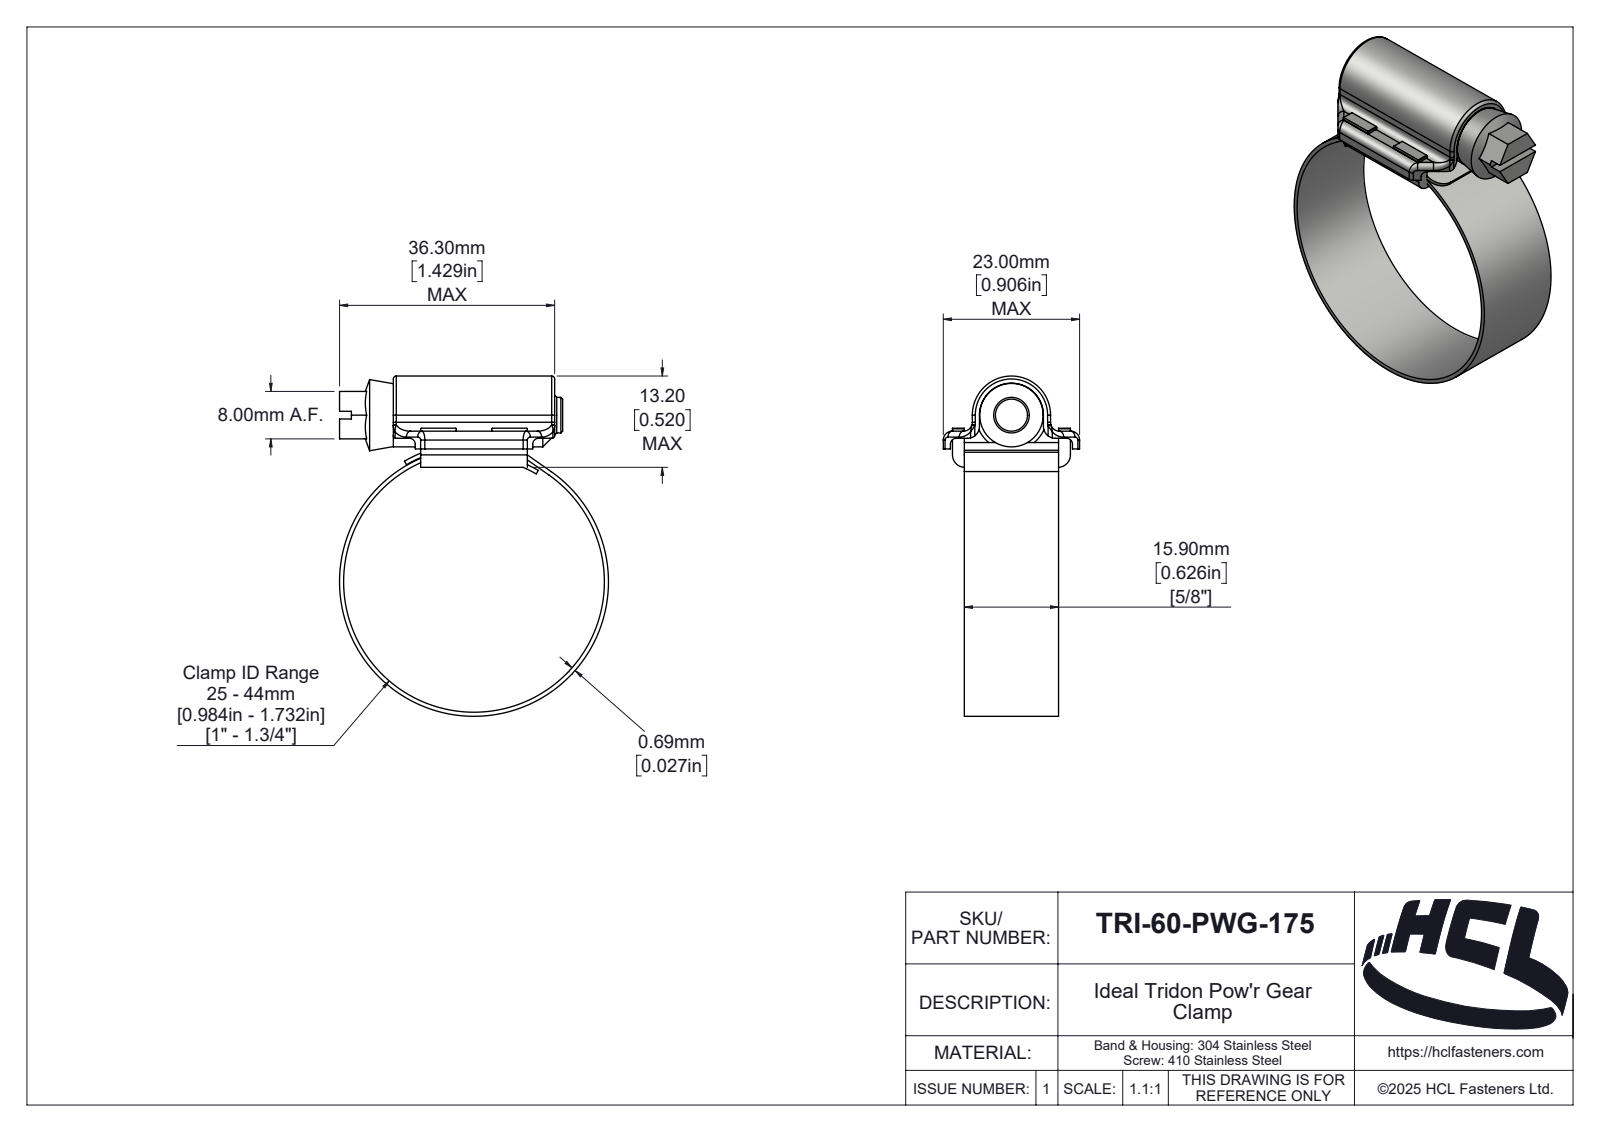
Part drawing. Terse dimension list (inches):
name: TRI-60-PWG-175
written by: SolidWorks 2025 (AUTOMOTIVE_DESIGN)
unit: in
bodies: 4 solids, 268 faces (87 planar, 102 cylindrical, 79 other)
size: 2.259 × 1.787 × 0.906
volume: 0.427 in³; area: 15.59 in²
holes: 1× ⌀1.732
bosses: 1× ⌀1.787, 1× ⌀0.421, 1× ⌀0.236
rounds: 14× R0.039, 4× R0.02, 4× R0.059, 3× R0.079, 2× R0.004, 2× R0.083, 2× R0.118, 1× R0.018
face distances: 0.079, 0.626, 0.705, 0.193, 0.047, 0.179, 0.132, 0.604, 0.1, 0.526
